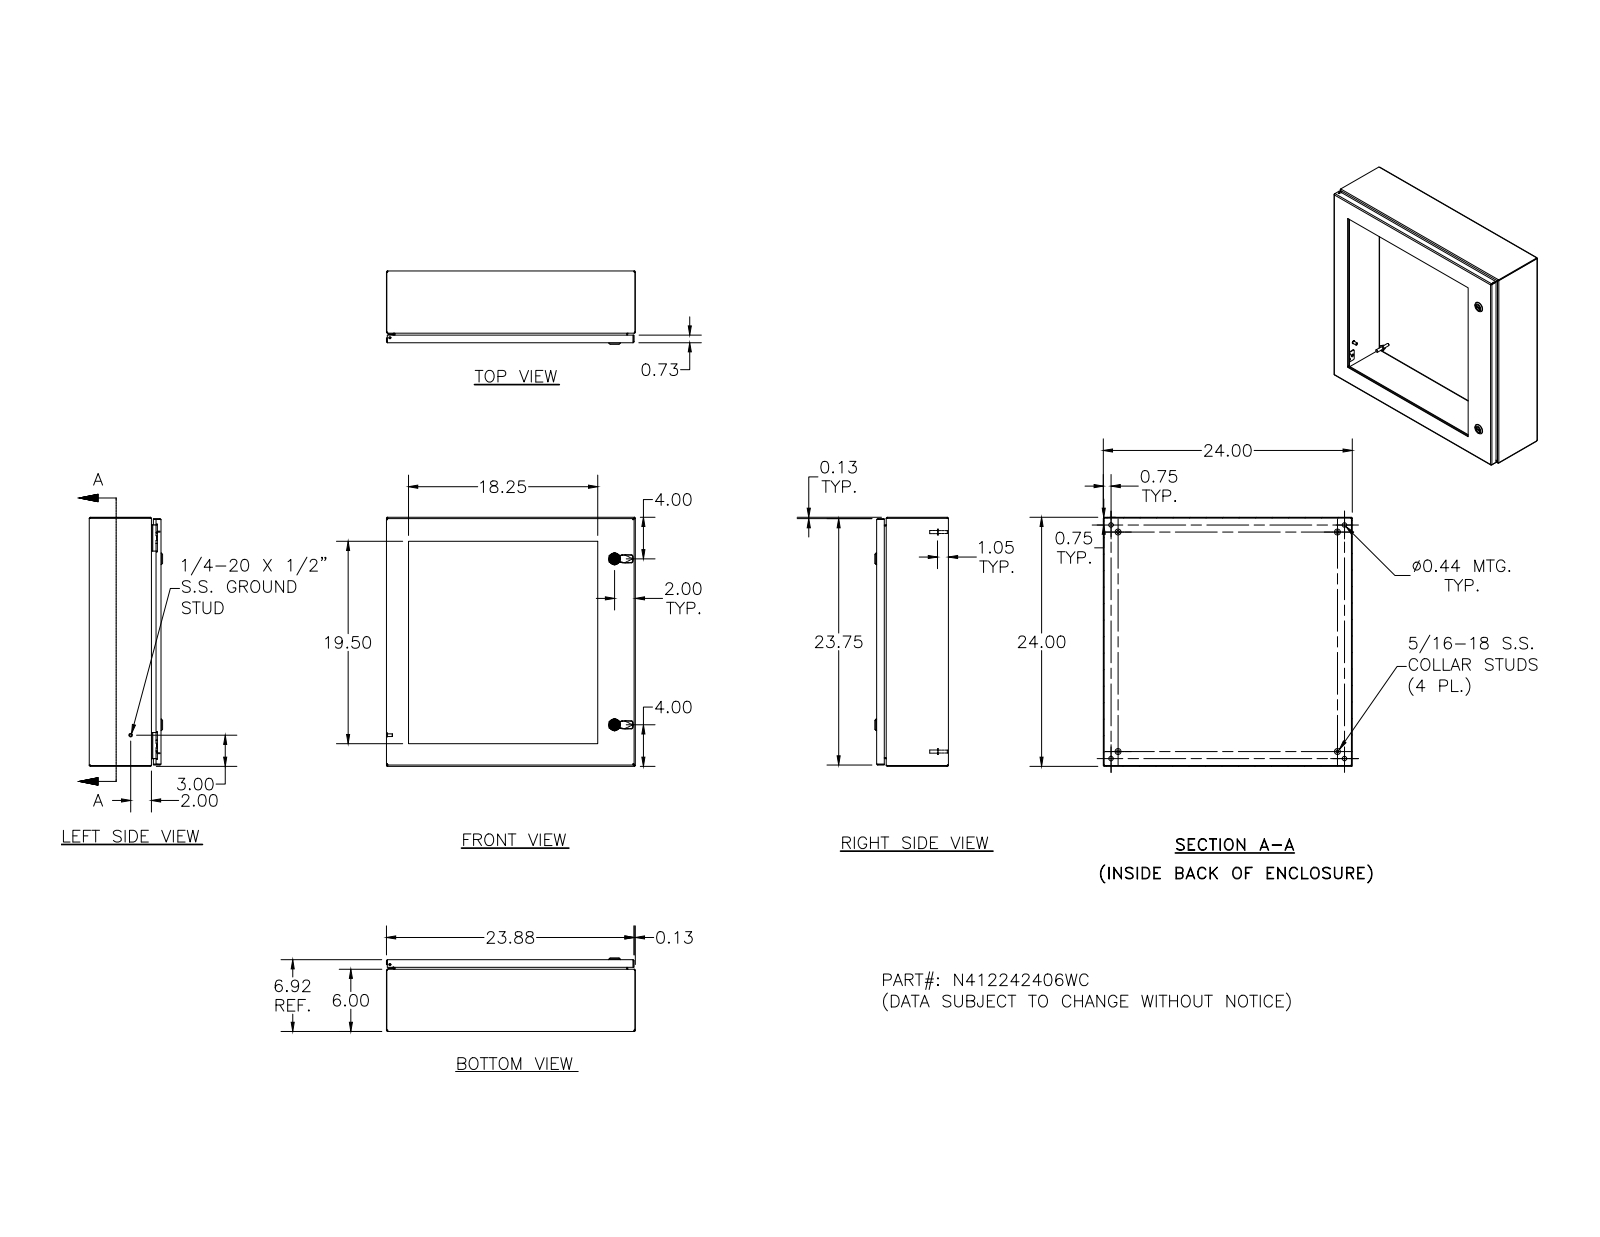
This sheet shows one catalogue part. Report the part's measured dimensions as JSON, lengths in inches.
{"part_name": "N412242406WC", "step_written_by": "SolidWorks 2018 (AUTOMOTIVE_DESIGN)", "units": "inches", "bodies": {"solids": 84, "faces": 2510, "planar": 971, "cylindrical": 762, "other": 777}, "overall_size": [24, 24, 7.075], "volume_in3": 221.9, "surface_area_in2": 4176, "round_holes": [[0.156, 22], [0.281, 20], [0.188, 5], [0.093, 4], [0.152, 4], [0.167, 4], [0.172, 4], [0.437, 4], [0.197, 2], [0.315, 2], [0.394, 2], [0.402, 2]], "round_bosses_or_shafts": [[0.337, 20], [0.19, 20], [0.25, 10], [0.563, 4], [0.36, 4], [0.32, 4], [0.3, 4], [0.275, 4]], "partial_cylinders_radius": [[0.012, 54], [0.031, 34], [0.05, 26], [0.105, 24], [0.02, 23], [0.016, 18], [0.125, 16], [0.032, 8]], "face_to_face_distances": [0.074, 6.843, 6.769, 23.926, 0.25, 6.593, 6.519, 24, 23.852, 6.917], "hole_center_spacings": [4, 8, 21.132, 12, 20, 22.239, 20.75, 6.221]}
